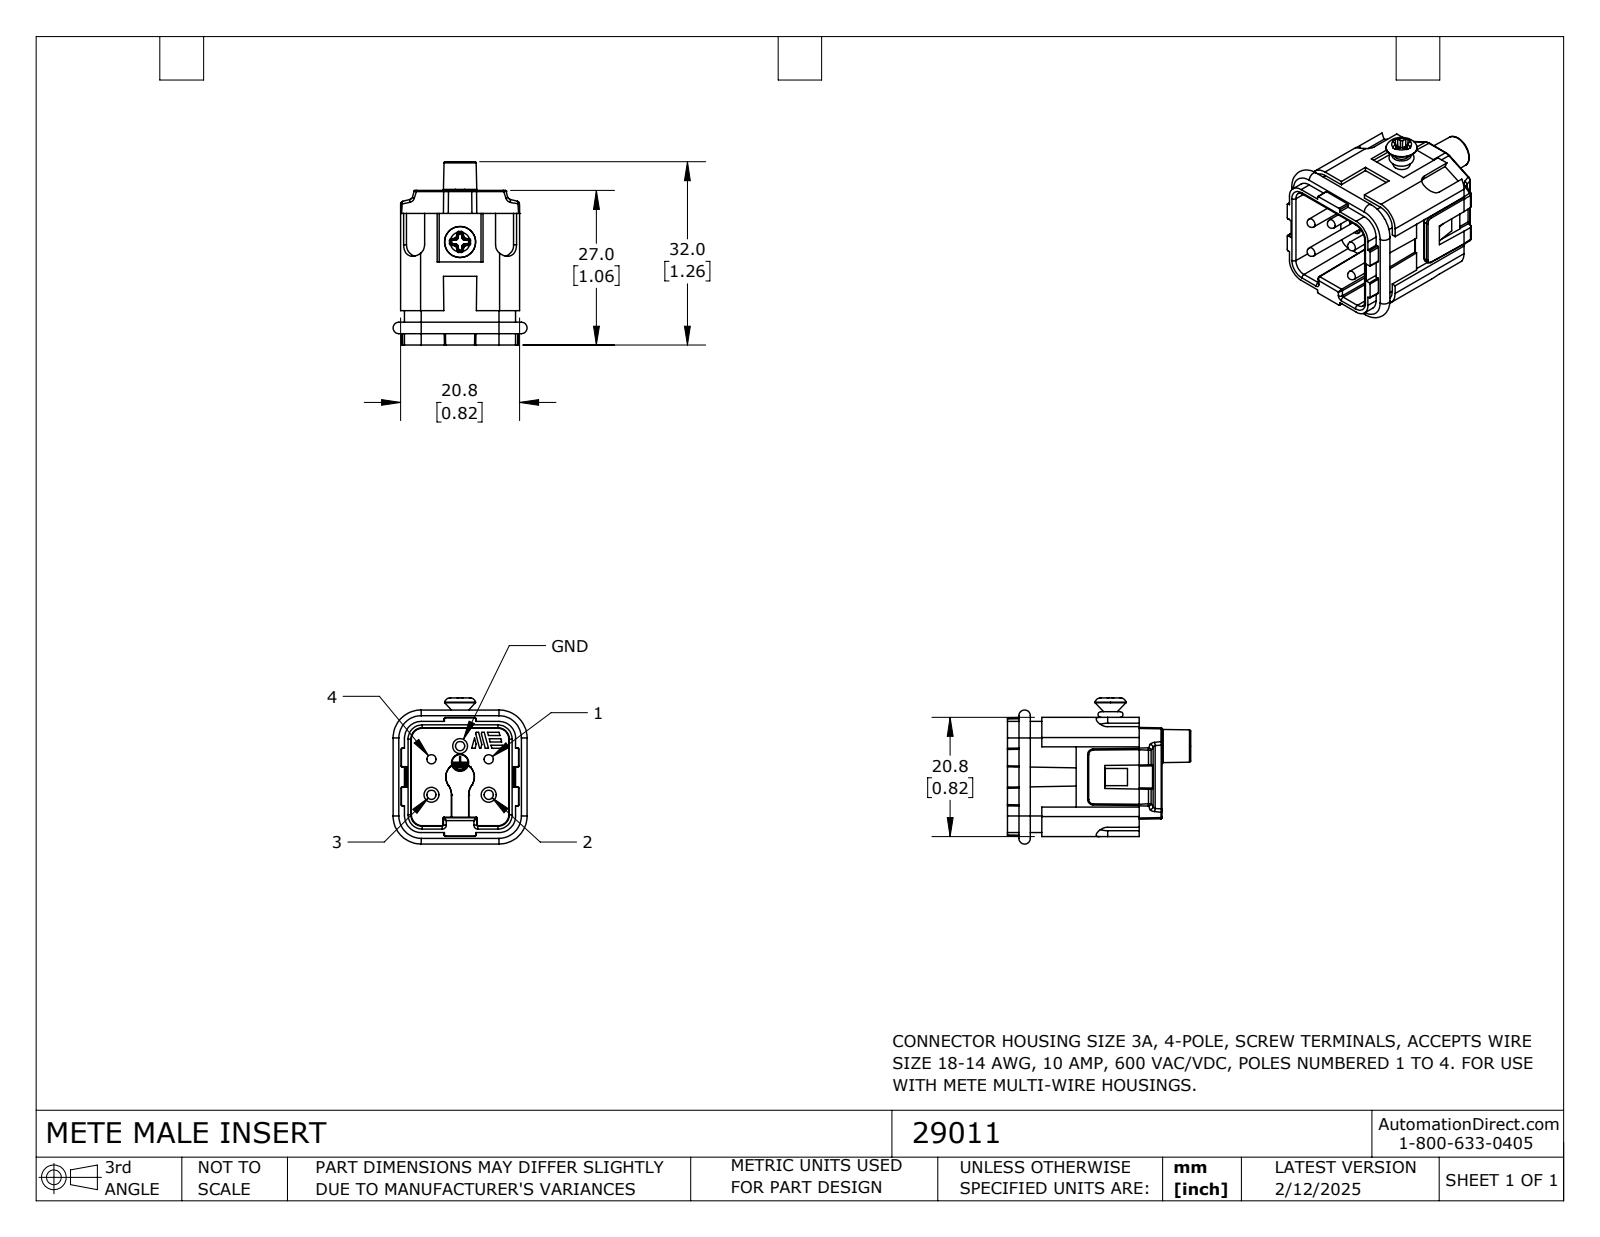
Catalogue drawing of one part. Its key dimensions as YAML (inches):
part_name: "29011"
step_written_by: "SolidWorks 2024 (CONFIG_CONTROL_DESIGN)"
units: inches
bodies: {solids: 1, faces: 641, planar: 283, cylindrical: 186, other: 172}
overall_size: [1.26, 1.004, 0.921]
volume: 0.422
surface_area: 8.188
round_holes:
  - {diameter: 0.102, count: 3}
  - {diameter: 0.11, count: 1}
  - {diameter: 0.122, count: 1}
round_bosses_or_shafts:
  - {diameter: 0.063, count: 5}
  - {diameter: 0.113, count: 4}
  - {diameter: 0.093, count: 3}
  - {diameter: 0.118, count: 1}
partial_cylinders:
  - {radius: 0.008, count: 46}
  - {radius: 0.02, count: 17}
  - {radius: 0.004, count: 12}
  - {radius: 0.012, count: 12}
  - {radius: 0.079, count: 9}
  - {radius: 0.039, count: 6}
  - {radius: 0.114, count: 5}
  - {radius: 0.016, count: 4}
face_to_face_distances: [0.453, 0.028, 0.791, 0.157, 0.079, 0.039, 0.748, 0.819, 0.74, 0.906]
hole_center_spacings: [0.296, 0.388, 0.114, 0.394]
